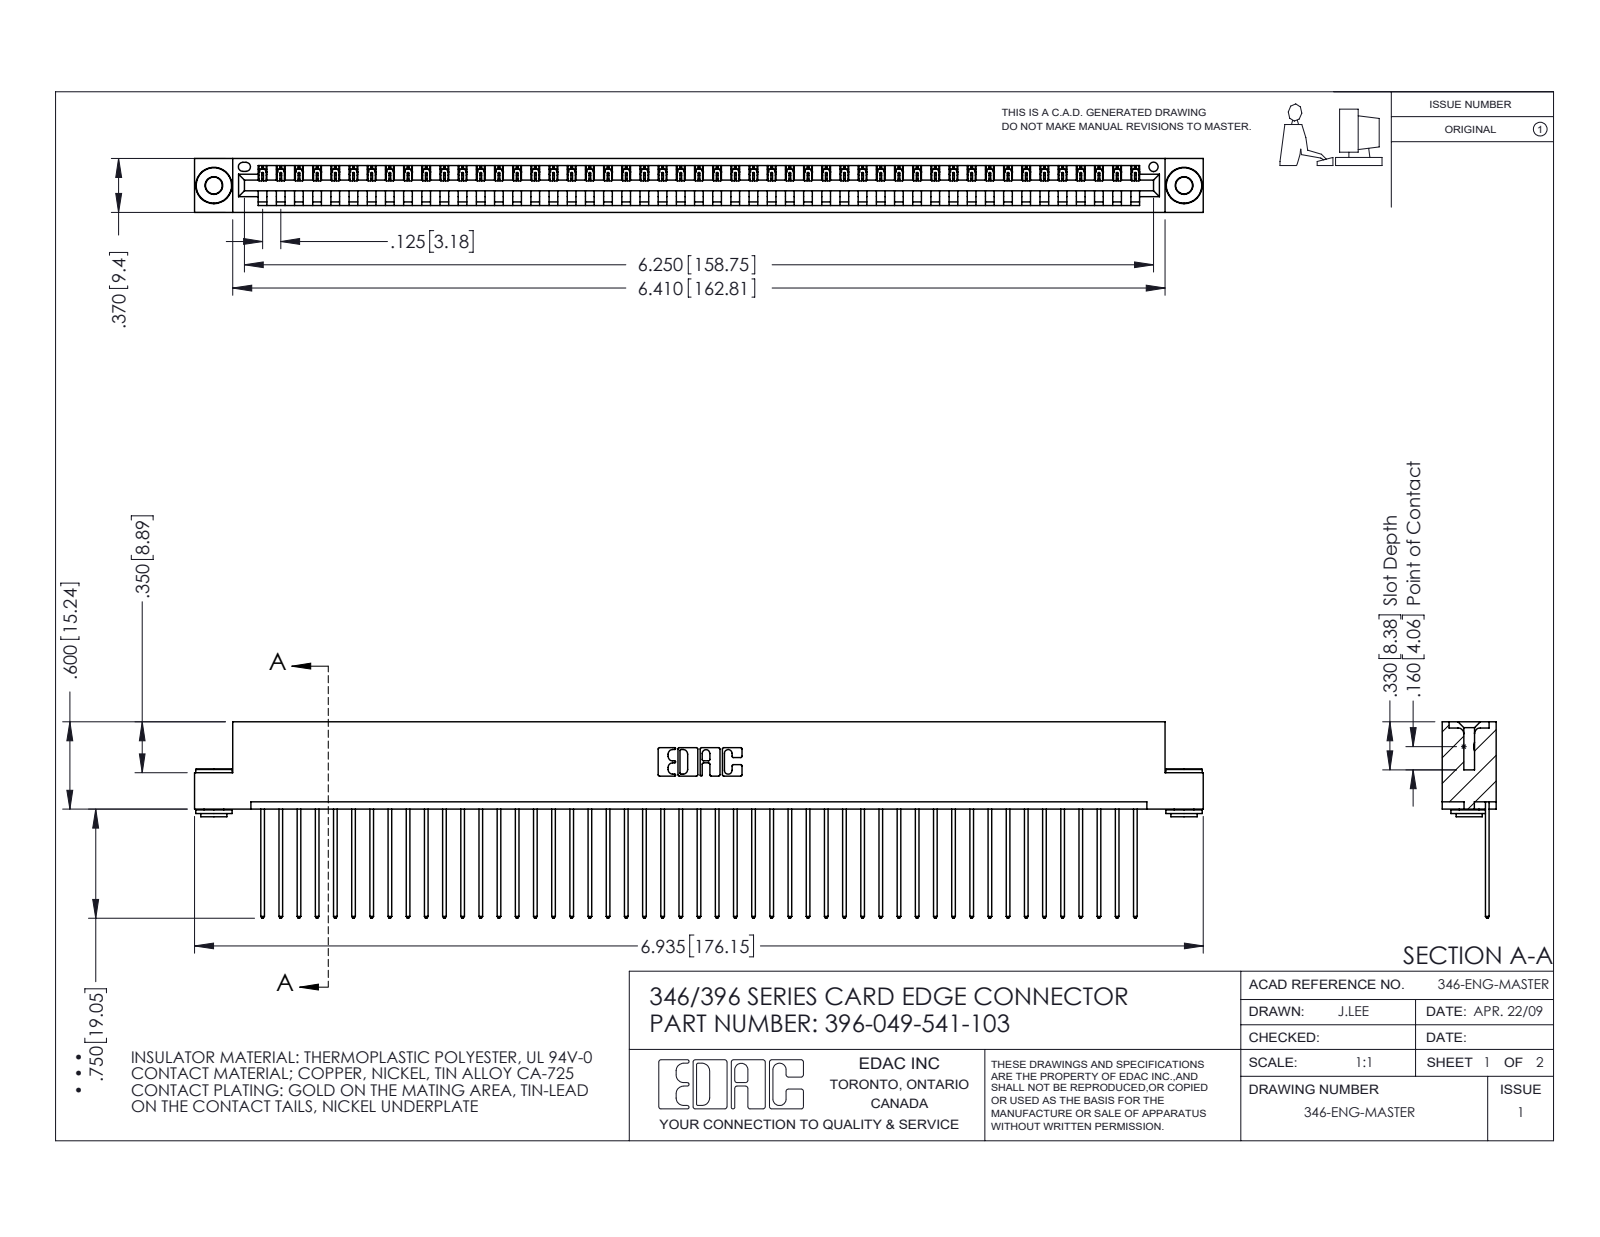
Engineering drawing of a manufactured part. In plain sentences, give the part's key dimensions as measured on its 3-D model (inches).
The part is named "346 Part_Flush Mounting Lugs - 0.156 Dia-TH; 345-292-001_345-293-141; 345-250-002_345-250-002-102; 396-049-541-103". Its 3-D file was written by "SolidWorks 2016 (CONFIG_CONTROL_DESIGN)". It is 52 solids with 3002 faces: 2046 planar, 948 cylindrical and 8 other. Overall it measures 6.935 by 1.35 by 0.37 inches. Its volume is 1.043 cubic inches and its surface area 35.06 square inches. Round holes: 2 of diameter 0.116, 2 of diameter 0.156, 1 of diameter 0.064. Round bosses or shafts: 2 of diameter 0.25, 2 of diameter 0.18, 2 of diameter 0.136. Partial cylindrical surfaces (rounded edges, fillets, slot ends): 98 of radius 0.006, 98 of radius 0.01, 22 of radius 0.01, 6 of radius 0.007, 6 of radius 0.031, 3 of radius 0.026, 2 of radius 0.031, 2 of radius 0.04. The main face-to-face distances are 0.048, 0.322, 0.37, 0.25, 0.025, 0.072, 0.298, 0.148, 0.222, 0.1. The hole center spacings are 0.246, 6.461, 6.67.
